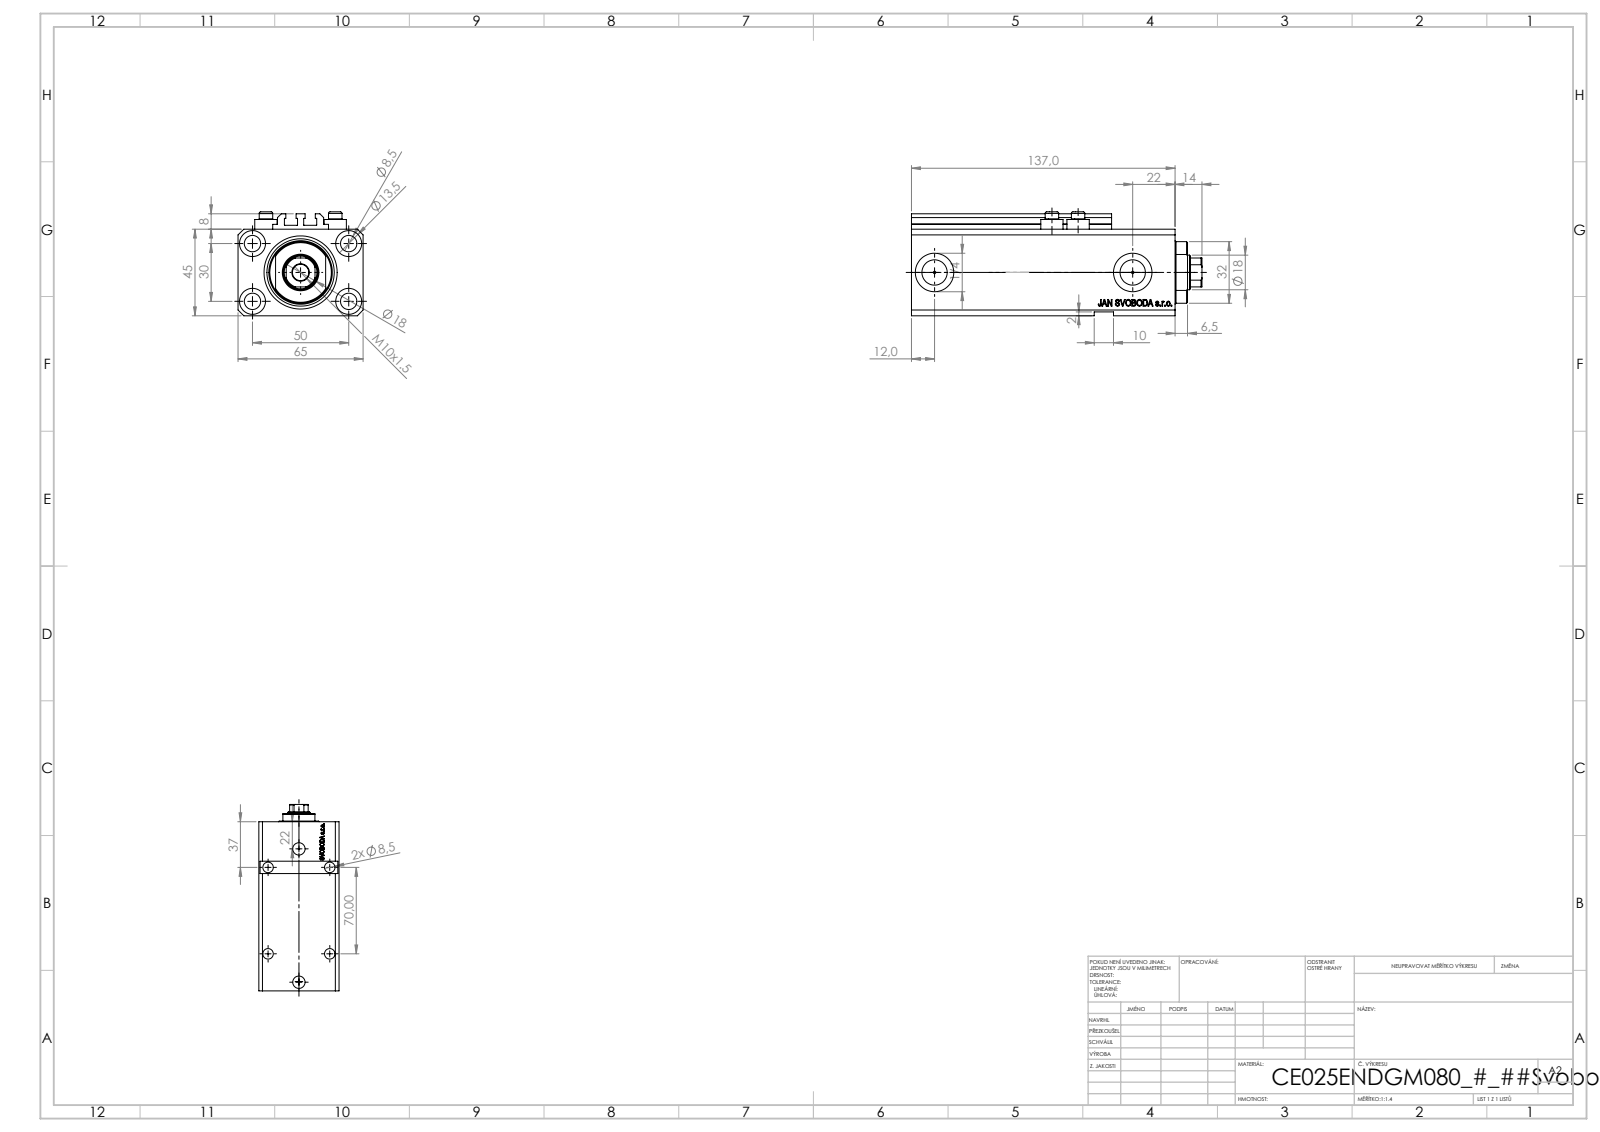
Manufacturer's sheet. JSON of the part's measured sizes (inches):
{"part_name": "V250CE_VC_E; V250CE_E_Body; ALLEN BOLT V250CE; V250CE_C_VCP", "step_written_by": "SolidWorks 2019 (CONFIG_CONTROL_DESIGN)", "units": "inches", "bodies": {"solids": 8, "faces": 1103, "planar": 515, "cylindrical": 158, "other": 430}, "overall_size": [5.945, 2.559, 2.126], "volume_in3": 21.17, "surface_area_in2": 146.8, "round_holes": [[0.335, 9], [0.049, 4], [0.157, 4], [0.531, 4], [0.394, 2], [0.518, 2], [0.787, 2], [0.709, 1], [0.984, 1], [1.496, 1]], "round_bosses_or_shafts": [[0.457, 4], [0.276, 4]], "partial_cylinders_radius": [[0.008, 10], [0.335, 1], [0.63, 1]], "face_to_face_distances": [1.772, 2.559, 1.85, 0.079, 4.843, 0.098, 0.551, 0.394, 0.803, 5.394], "hole_center_spacings": [1.148, 1.969, 0.535, 0.595, 1.098, 1.181, 1.323, 1.324]}
